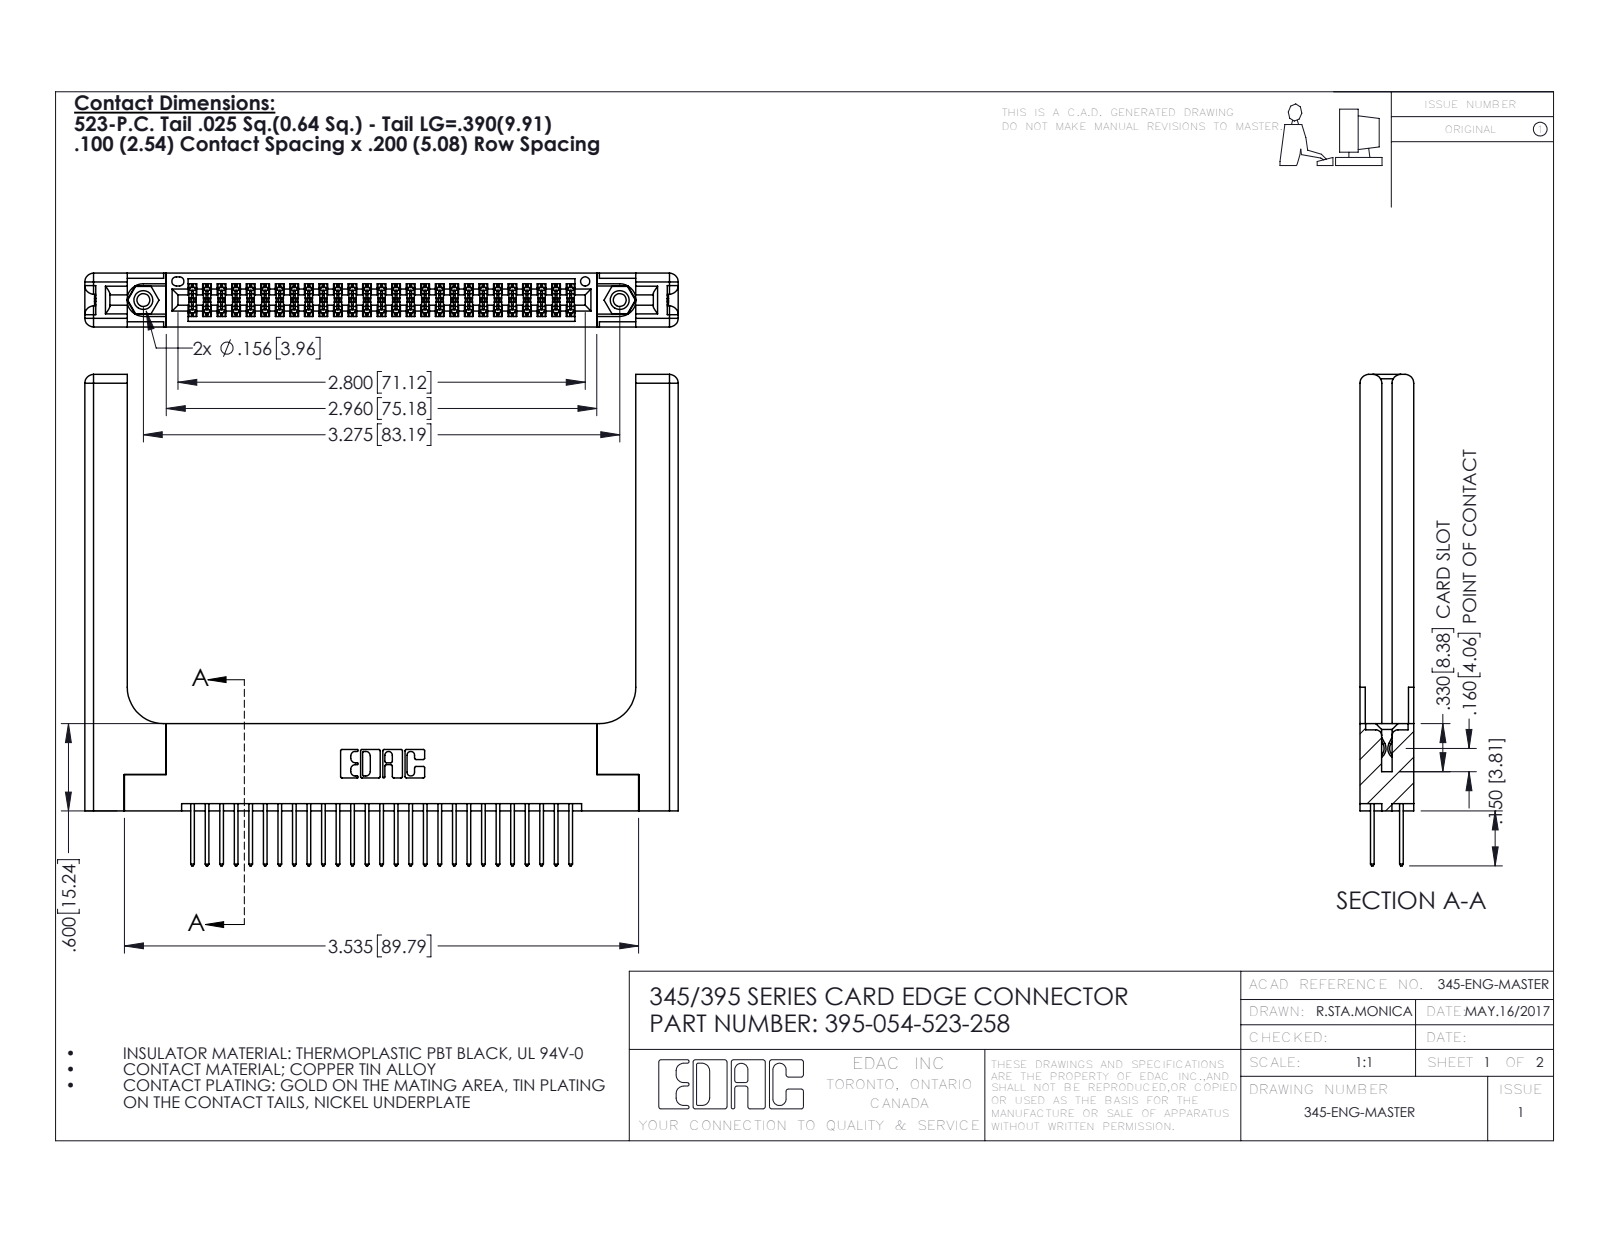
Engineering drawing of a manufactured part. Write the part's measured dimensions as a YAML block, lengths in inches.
part_name: "345-292-001_345-293-123; 395-054-523-258; 345-220-058_345-220-058; 345 Part_Flush Mounting Lugs - 0.156 Dia-TH (+1 more)"
step_written_by: "SolidWorks 2016 (CONFIG_CONTROL_DESIGN)"
units: inches
bodies: {solids: 59, faces: 3082, planar: 2010, cylindrical: 1012, other: 60}
overall_size: [4.079, 3.377, 0.37]
volume: 1.13
surface_area: 31.15
round_holes:
  - {diameter: 0.089, count: 2}
  - {diameter: 0.125, count: 2}
  - {diameter: 0.156, count: 2}
  - {diameter: 0.064, count: 1}
round_bosses_or_shafts:
  - {diameter: 0.155, count: 2}
partial_cylinders:
  - {radius: 0.006, count: 81}
  - {radius: 0.01, count: 54}
  - {radius: 0.01, count: 22}
  - {radius: 0.06, count: 16}
  - {radius: 0.007, count: 6}
  - {radius: 0.031, count: 6}
  - {radius: 0.026, count: 3}
  - {radius: 0.014, count: 2}
face_to_face_distances: [0.072, 0.37, 0.298, 0.2, 0.098, 0.272, 0.025, 0.225, 0.148, 0.15]
hole_center_spacings: [0.27, 3.04, 3.275]
